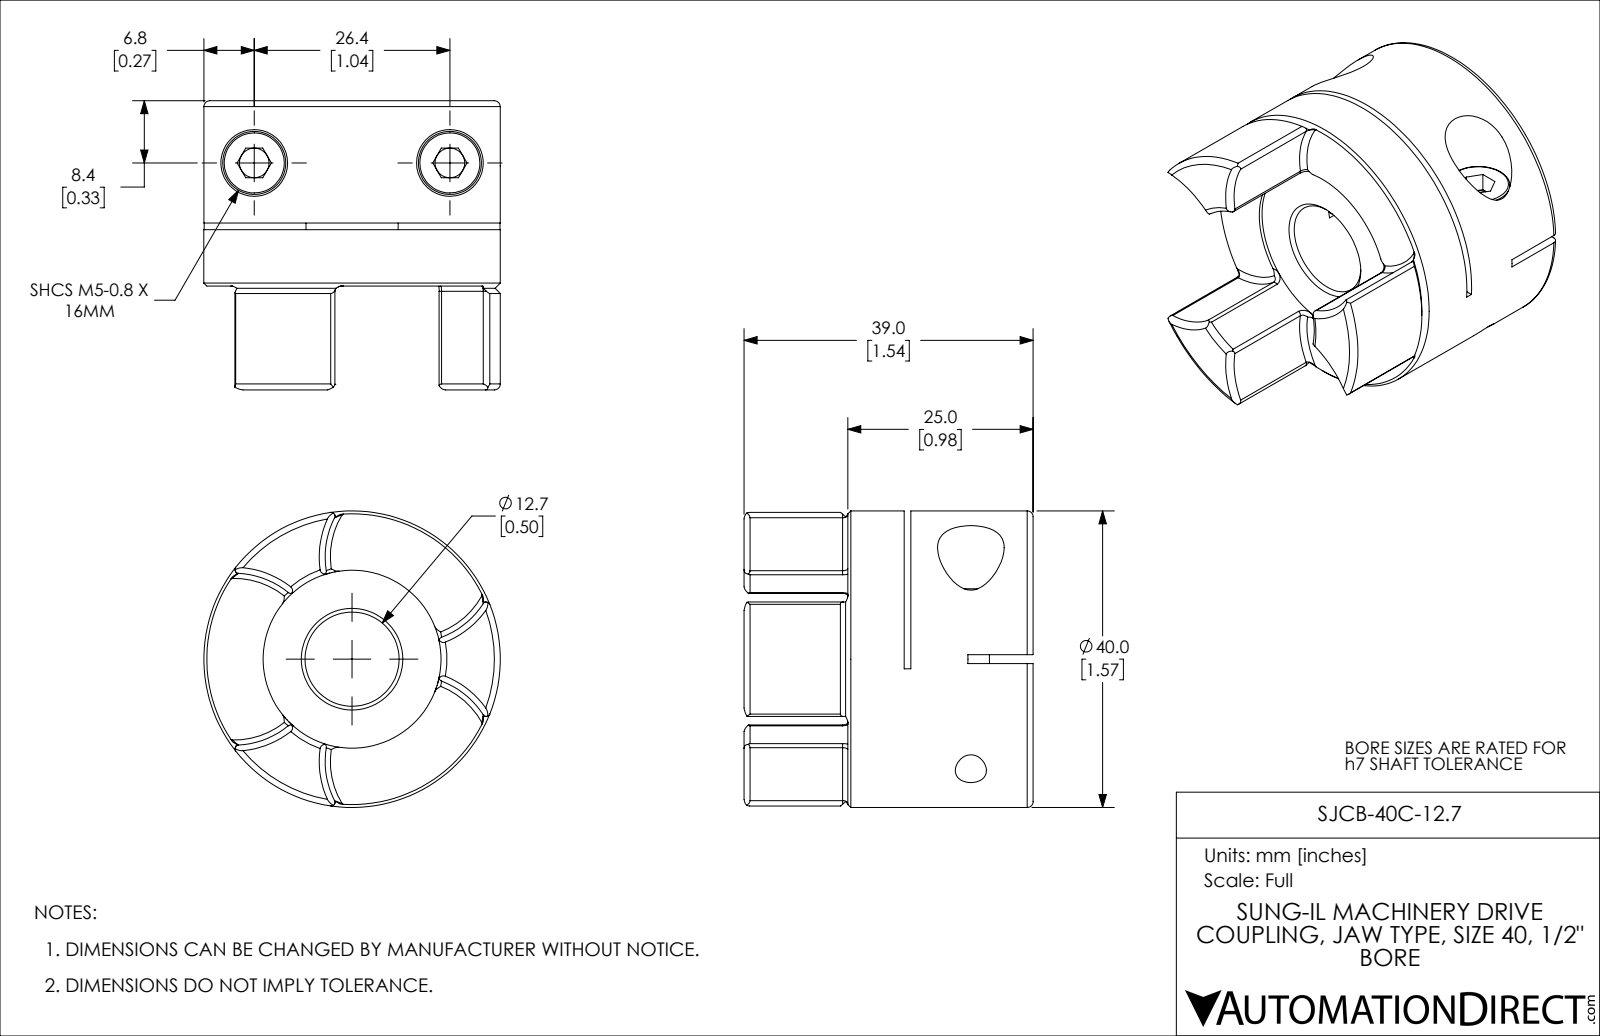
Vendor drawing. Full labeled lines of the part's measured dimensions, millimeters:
Part name (STEP PRODUCT): SJCB-40C-12
STEP written by: SolidWorks 2021 (CONFIG_CONTROL_DESIGN)
Units: millimetres
Bodies: 3 solids, 184 faces (50 planar, 68 cylindrical, 66 other)
Overall size (bounding box): 40 × 40 × 39
Volume: 29 948 mm³ · Surface area: 11 686 mm²
Round holes (diameter × count): ⌀4 ×2, ⌀4.2 ×2, ⌀5.4 ×2, ⌀9 ×2, ⌀12 ×1, ⌀24 ×1
Round bosses / shafts (diameter × count): ⌀8.5 ×2, ⌀5 ×2, ⌀40 ×1
Partial cylindrical surfaces — rounded edges, fillets, slot ends (radius × count): R0.5 ×12, R11.6 ×3, R40 ×1
Main face-to-face distances: 17.4, 0.9, 16.5, 7.6, 8.5, 25, 1.2, 0.5, 7.1, 8
Hole centre spacings: 26.4
